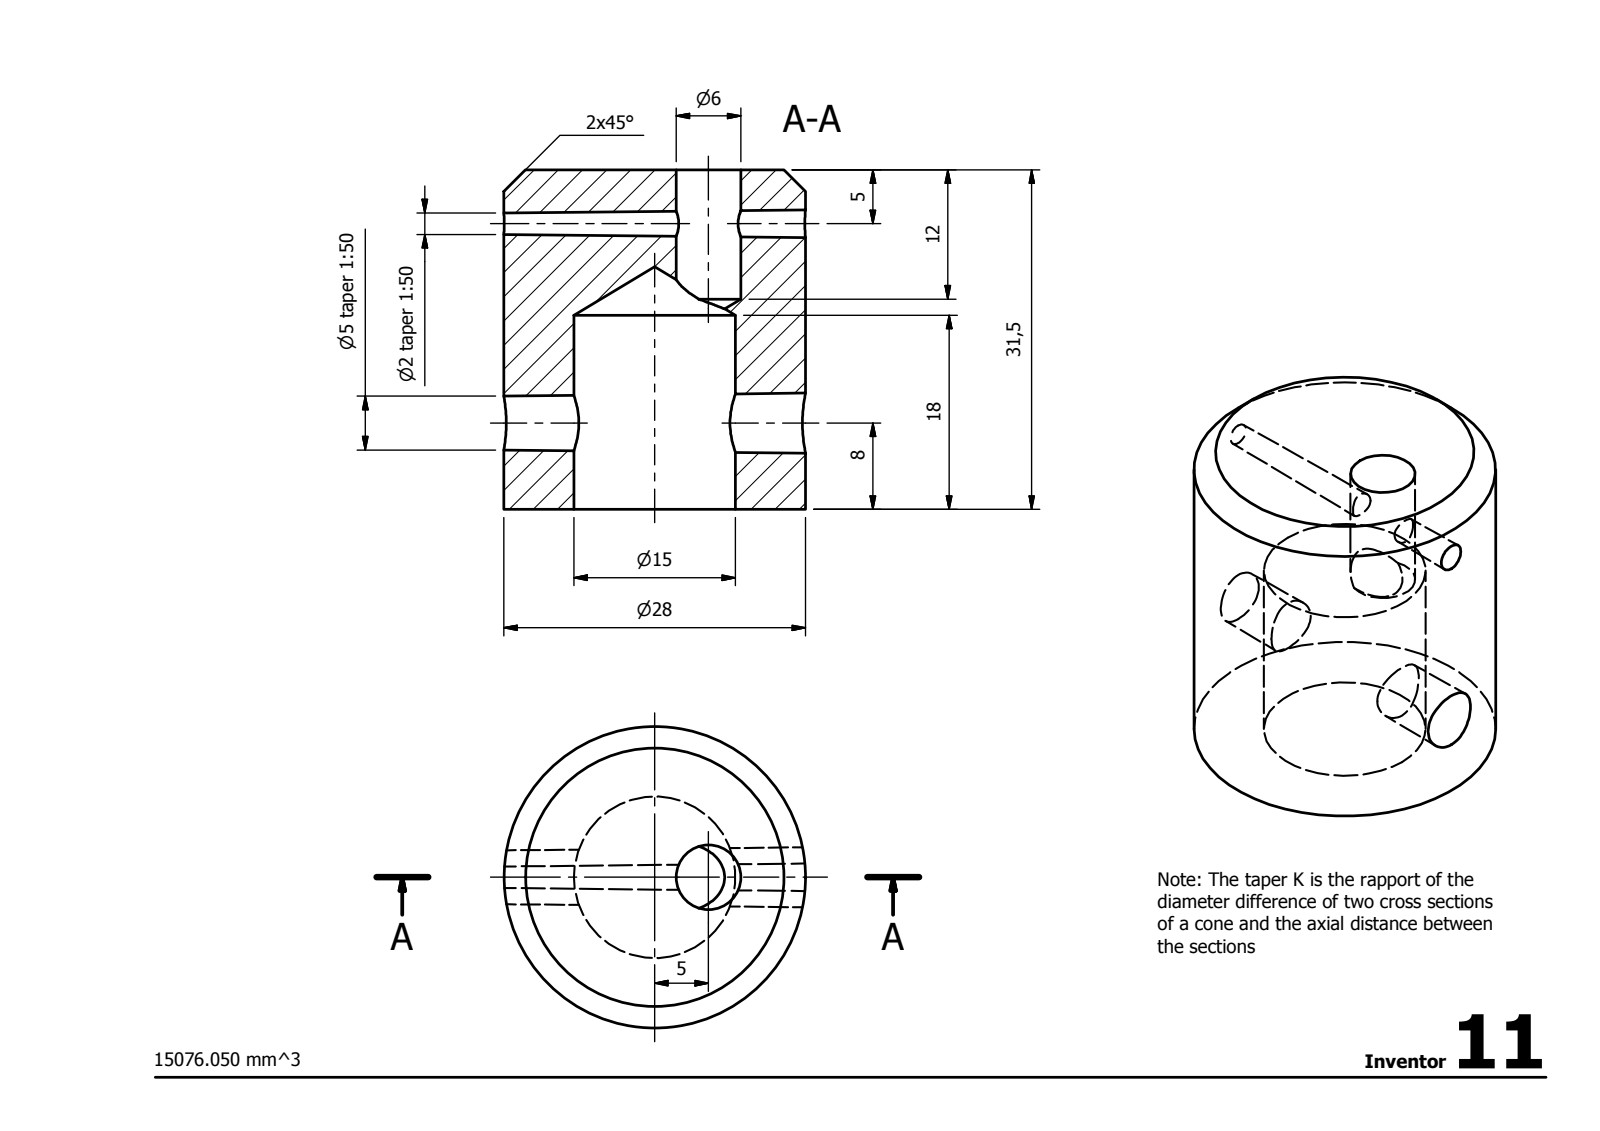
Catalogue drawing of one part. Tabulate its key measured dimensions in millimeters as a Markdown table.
| quantity | value |
| --- | --- |
| STEP written by | Autodesk Inventor 2014 (AUTOMOTIVE_DESIGN) |
| units | millimeters |
| bodies | 1 solid, 13 faces (2 planar, 3 cylindrical, 8 other) |
| overall size | 31.5 × 28 × 28 |
| volume | 15 324 mm³ |
| surface area | 5 059 mm² |
| round holes (diameter × count) | 6 × 1, 15 × 1 |
| round bosses / shafts (diameter × count) | 28 × 1 |
| main face-to-face distances | 31.5 |
| hole center spacings | 5 |
